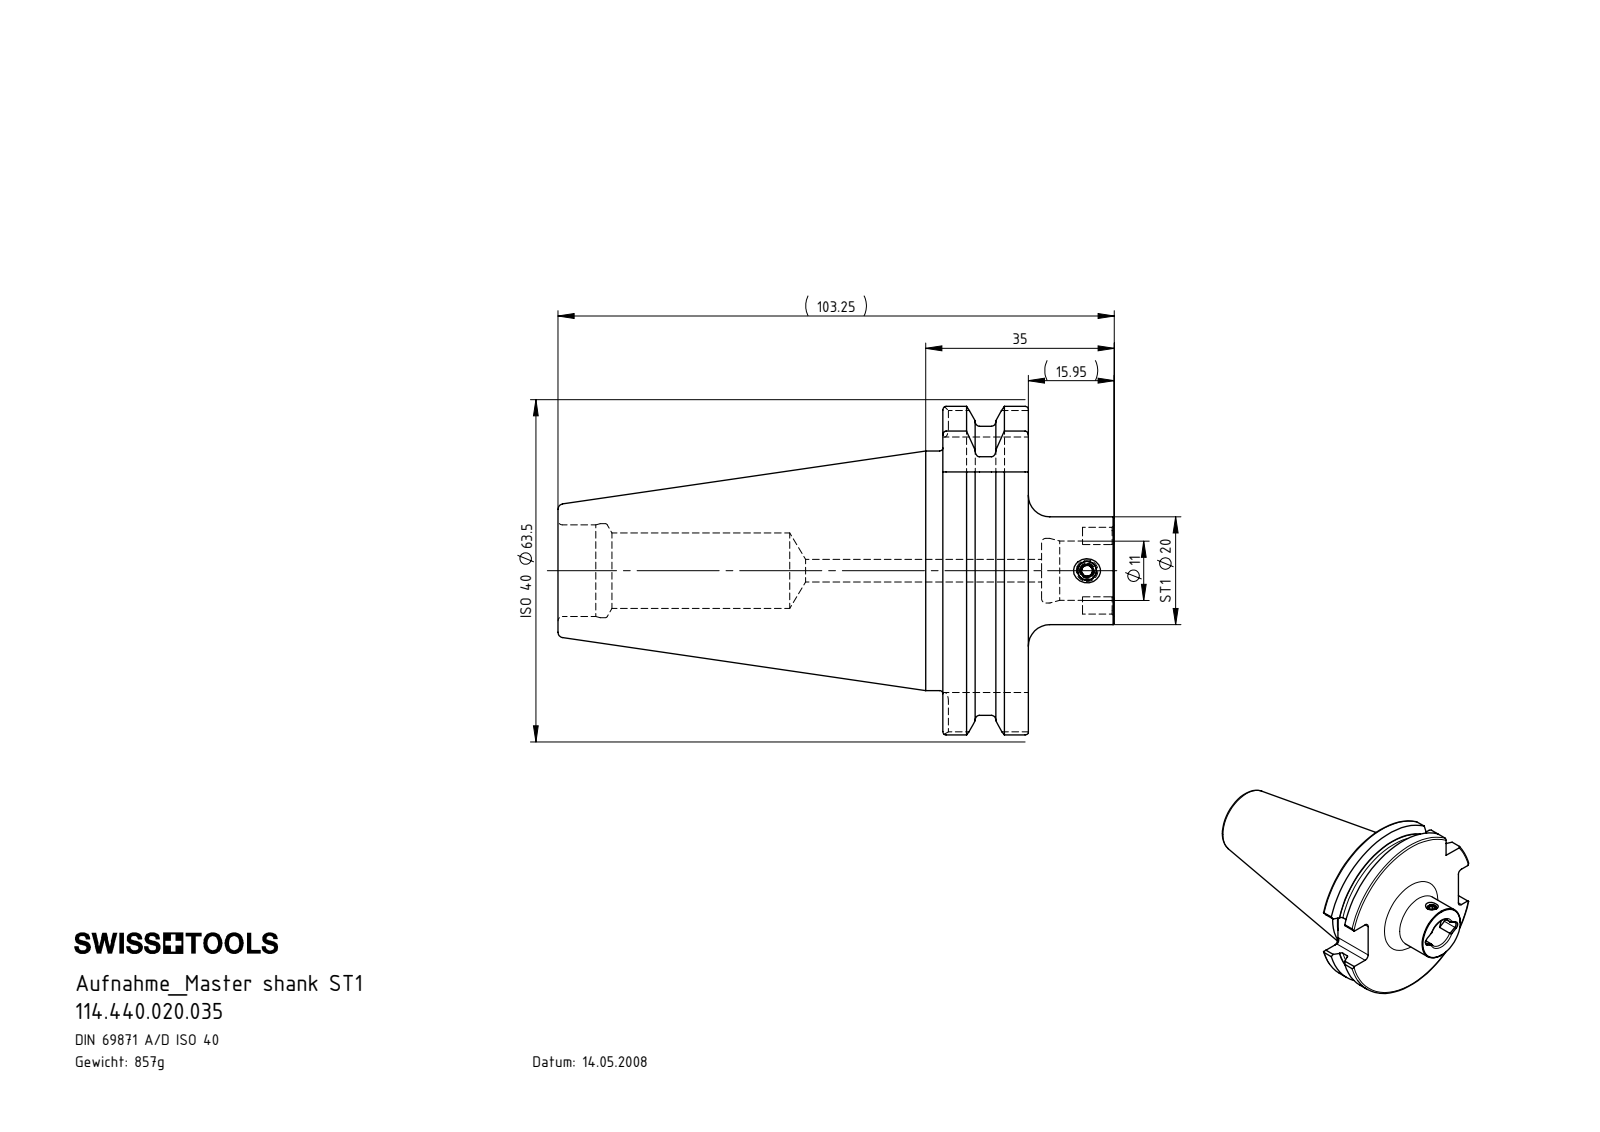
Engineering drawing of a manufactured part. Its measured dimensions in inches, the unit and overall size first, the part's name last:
Units: inches
Overall size (bounding box): 4.065 × 2.5 × 2.399
Round holes (diameter × count): ⌀0.079 ×1, ⌀0.138 ×1, ⌀0.165 ×1, ⌀0.433 ×1, ⌀0.472 ×1, ⌀0.551 ×1, ⌀0.669 ×1, ⌀0.687 ×1
Round bosses / shafts (diameter × count): ⌀1.75 ×1, ⌀0.787 ×1, ⌀0.157 ×1
Partial cylindrical surfaces — rounded edges, fillets, slot ends (radius × count): R0.063 ×8, R0.051 ×2, R1.102 ×1, R1.25 ×1
Main face-to-face distances: 0.624, 1.866, 1.252, 0.628, 2.813, 3.437, 4.065, 0.634, 1.039, 0.406
Volume: 6.662 in³ · Surface area: 31.86 in²
Bodies: 2 solids, 126 faces (54 planar, 30 cylindrical, 42 other)
Part name (STEP PRODUCT): SK4.ST1.K01.035; ST1-ER1.001.005_A; SK4-ST1.K01.035-B
STEP written by: SolidWorks 2017 (AUTOMOTIVE_DESIGN)
